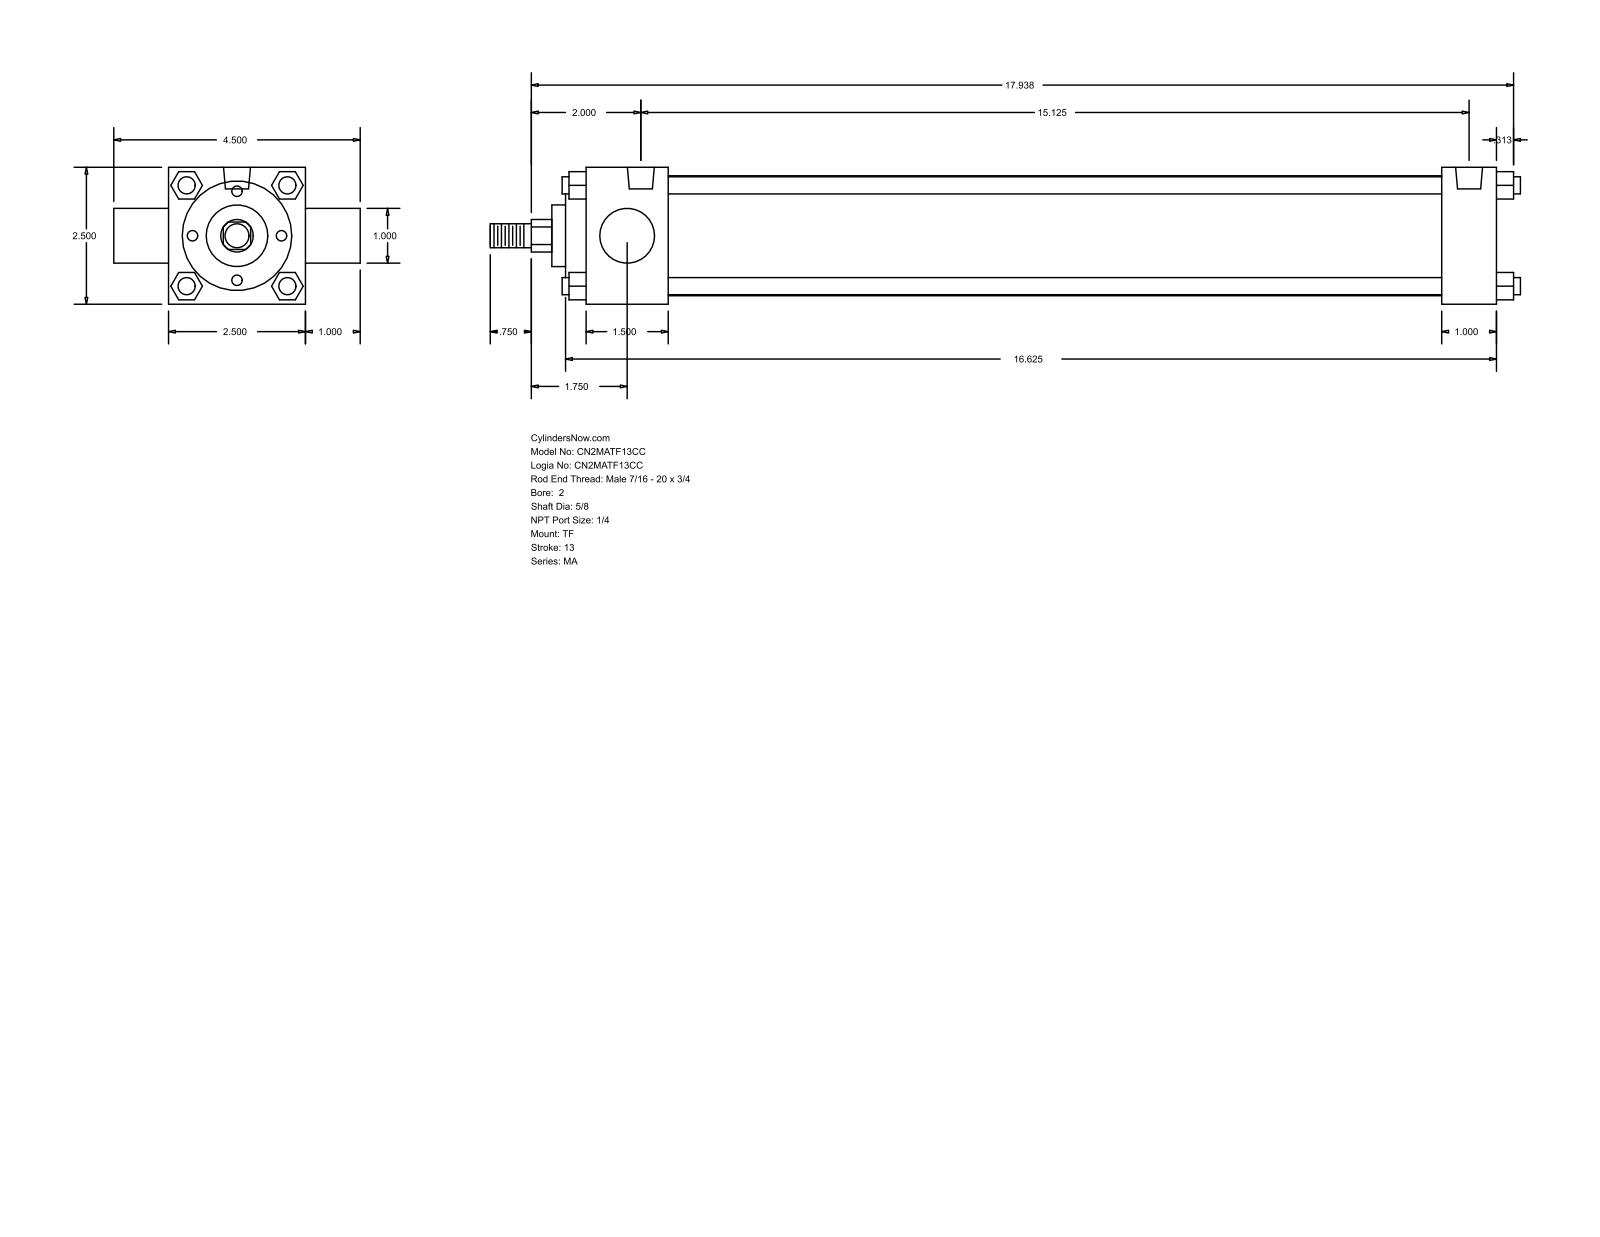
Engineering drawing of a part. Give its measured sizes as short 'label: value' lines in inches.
name: MA_TF__0200_0.625
written by: GSSL Pune (CONFIG_CONTROL_DESIGN)
unit: in
bodies: 0 solids, 122 faces (93 planar, 29 cylindrical, 0 other)
size: 18.813 × 4.5 × 2.5
holes: 3× ⌀0.313, 2× ⌀0.492
bosses: 4× ⌀0.313, 1× ⌀2.19, 1× ⌀2, 1× ⌀1.125, 1× ⌀1, 1× ⌀0.625, 1× ⌀0.437
rounds: 1× R0.297
face distances: 2.5, 1.5, 0.5, 16.625, 15.625, 14.125, 15.125, 1, 0.375, 1.875
hole spacings: 15.125
